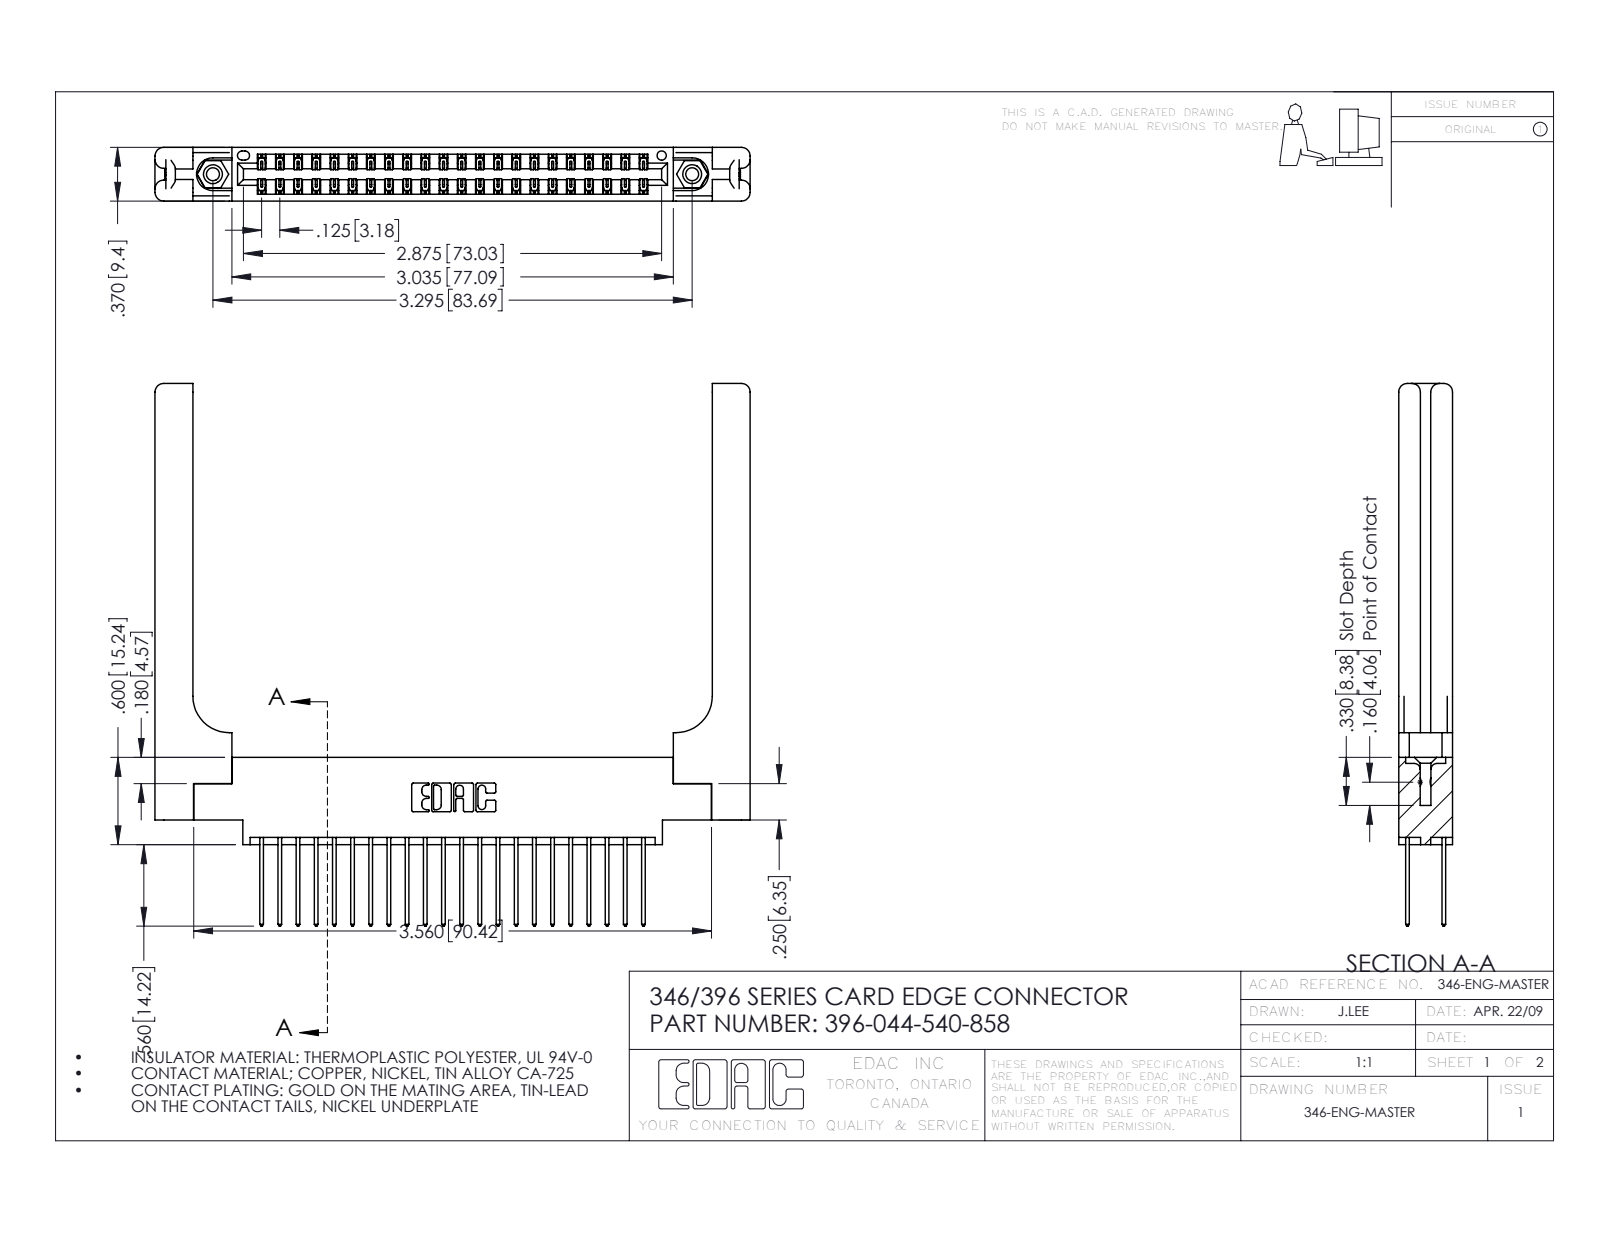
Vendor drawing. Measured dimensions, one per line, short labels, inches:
name: 345-250-001_345-250-001-102; 396-044-540-858; 345-292-001_345-293-140; 346 Part_0.170 Offset - 0.156 Dia-TH (+1 more)
written by: SolidWorks 2016 (CONFIG_CONTROL_DESIGN)
unit: in
bodies: 49 solids, 2670 faces (1768 planar, 842 cylindrical, 60 other)
size: 4.091 × 3.73 × 0.37
volume: 1.067 in³; area: 30.01 in²
holes: 2× ⌀0.089, 2× ⌀0.125, 2× ⌀0.156, 1× ⌀0.064
bosses: 2× ⌀0.155
rounds: 66× R0.006, 44× R0.01, 22× R0.01, 16× R0.06, 6× R0.007, 6× R0.031, 3× R0.026, 2× R0.014
face distances: 0.37, 0.072, 0.048, 0.322, 0.25, 0.148, 0.15, 0.025, 0.298, 0.275
hole spacings: 0.246, 3.087, 3.295
